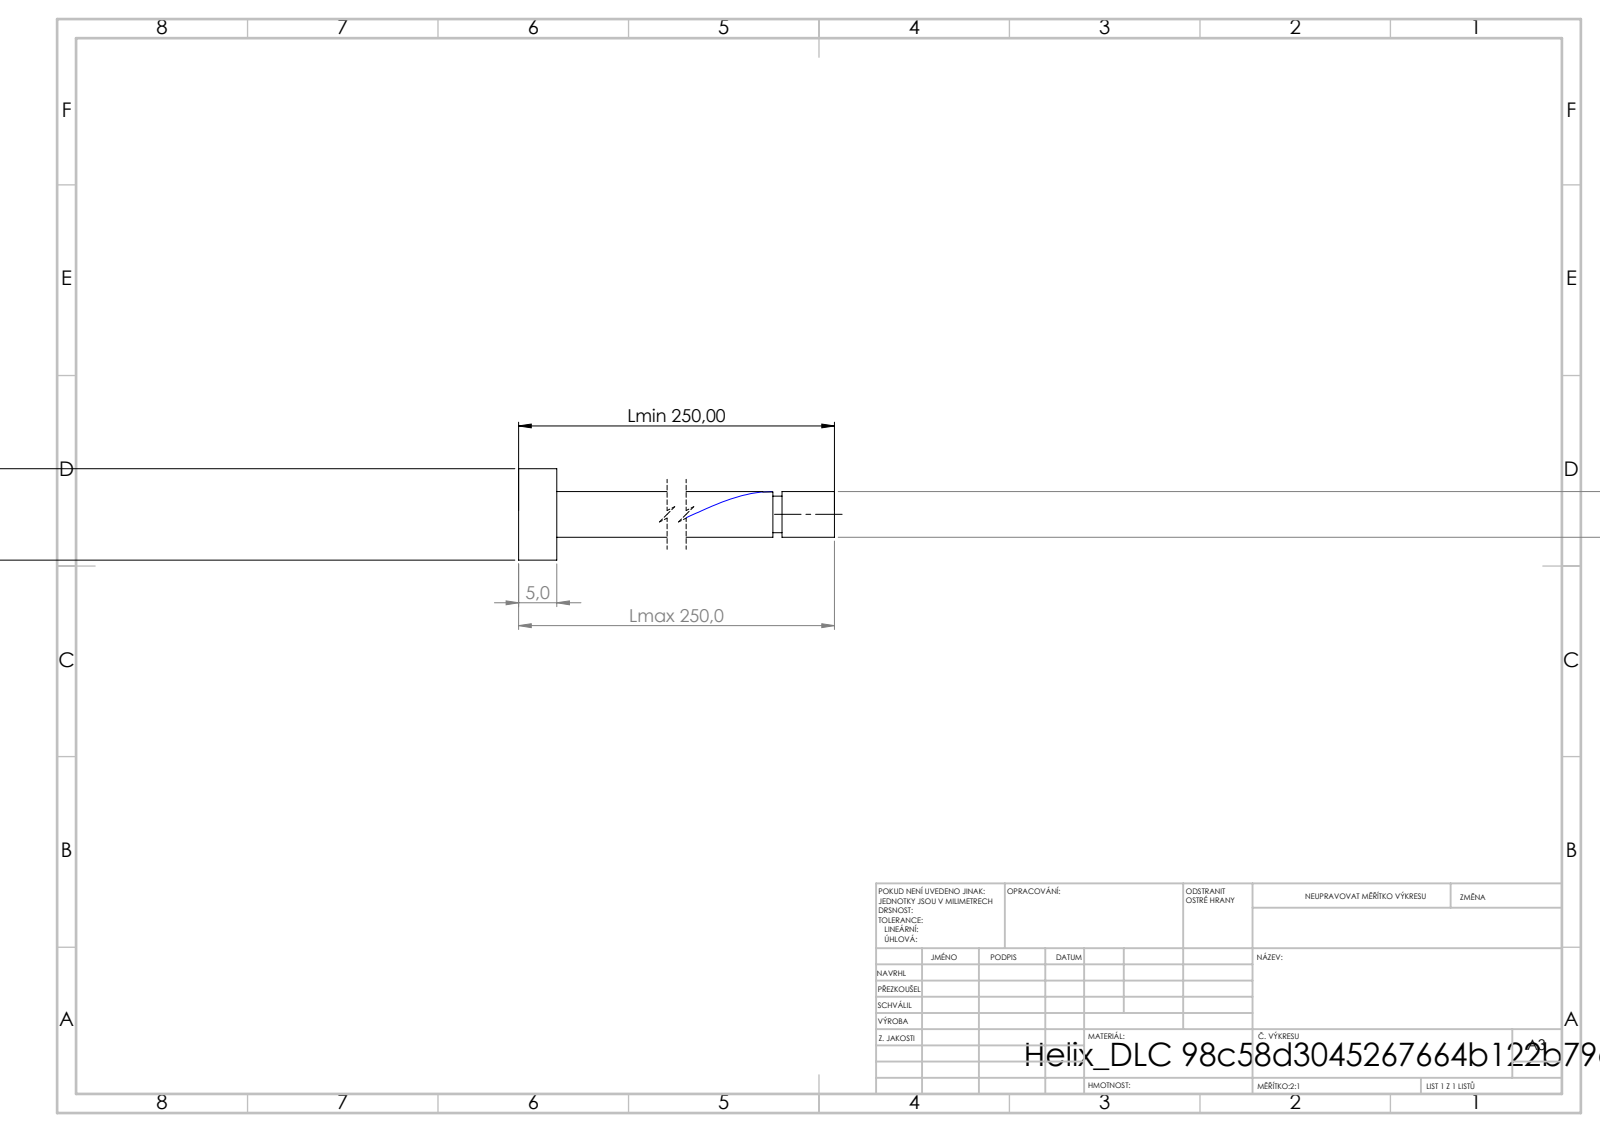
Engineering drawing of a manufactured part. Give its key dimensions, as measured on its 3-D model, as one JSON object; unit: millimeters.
{"step_written_by": "SolidWorks 2019 (CONFIG_CONTROL_DESIGN)", "units": "millimeters", "bodies": {"solids": 1, "faces": 21, "planar": 6, "cylindrical": 14, "other": 1}, "overall_size": [250, 12, 12], "volume_mm3": 7413, "surface_area_mm2": 5129, "round_bosses_or_shafts": [[12, 1], [6, 1], [4.8, 1]], "face_to_face_distances": [5, 250, 245, 243.12, 238.12, 6.88, 241.92, 236.92, 1.2, 8.08]}
